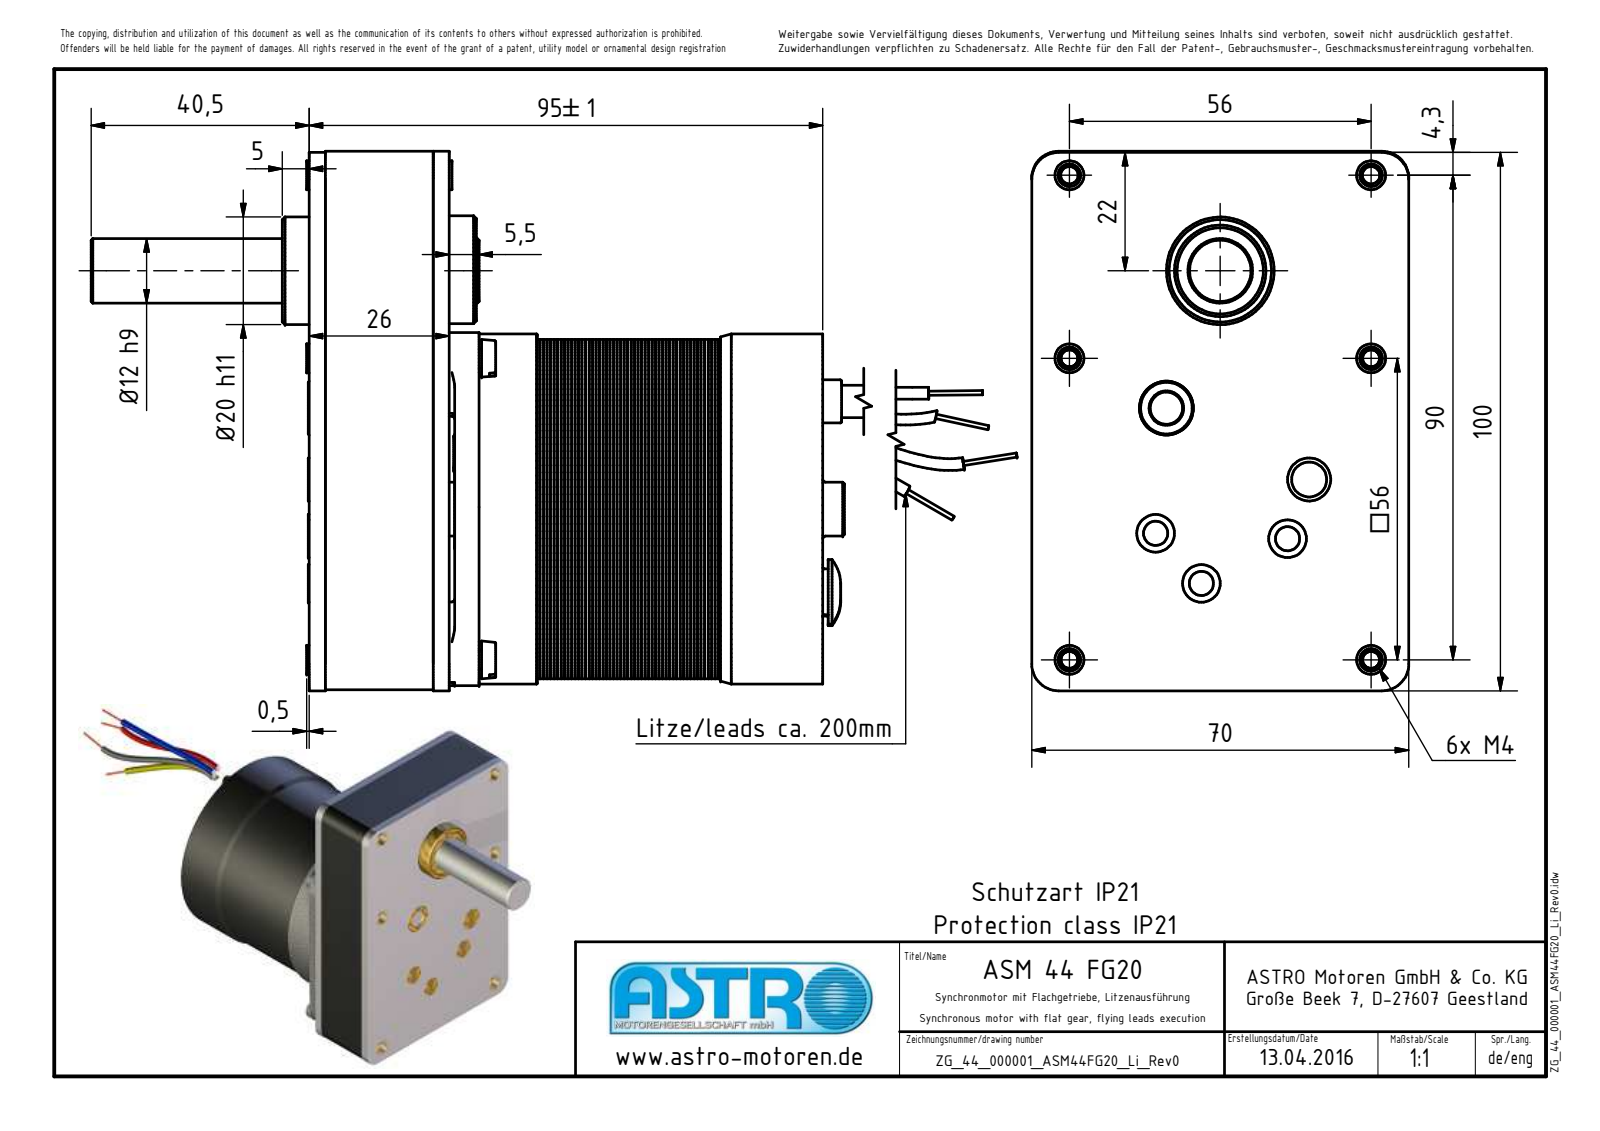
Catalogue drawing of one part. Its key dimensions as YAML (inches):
part_name: "ZG_44_000001_ASM44FG20_Li_Rev0; AFG-20rund; FG-Antriebsseite20; FG-Abstandhalter (+8 more)"
step_written_by: "Autodesk Inventor 2010 (AUTOMOTIVE_DESIGN)"
units: inches
bodies: {solids: 94, faces: 9256, planar: 3390, cylindrical: 5661, other: 205}
overall_size: [8.369, 3.945, 2.756]
volume: 10.23
surface_area: 413.9
round_holes:
  - {diameter: 0.063, count: 8}
  - {diameter: 0.161, count: 8}
  - {diameter: 0.197, count: 7}
  - {diameter: 0.173, count: 4}
  - {diameter: 0.177, count: 3}
  - {diameter: 0.394, count: 3}
  - {diameter: 0.63, count: 3}
  - {diameter: 0.236, count: 2}
  - {diameter: 0.217, count: 1}
  - {diameter: 0.256, count: 1}
  - {diameter: 0.472, count: 1}
  - {diameter: 0.551, count: 1}
round_bosses_or_shafts:
  - {diameter: 0.315, count: 8}
  - {diameter: 0.157, count: 8}
  - {diameter: 0.212, count: 6}
  - {diameter: 0.191, count: 6}
  - {diameter: 0.591, count: 4}
  - {diameter: 0.143, count: 4}
  - {diameter: 0.141, count: 4}
  - {diameter: 0.276, count: 3}
partial_cylinders:
  - {radius: 0.02, count: 32}
  - {radius: 0.089, count: 8}
  - {radius: 0.138, count: 8}
  - {radius: 0.197, count: 8}
  - {radius: 0.124, count: 4}
  - {radius: 0.207, count: 4}
  - {radius: 0.433, count: 1}
  - {radius: 1.122, count: 1}
face_to_face_distances: [0.026, 0.051, 0.077, 0.118, 0.102, 0.128, 0.906, 0.154, 0.179, 0.787]
hole_center_spacings: [1.239, 0.444, 1.161, 1.643, 1.85, 2.182, 2.205, 0.889]
